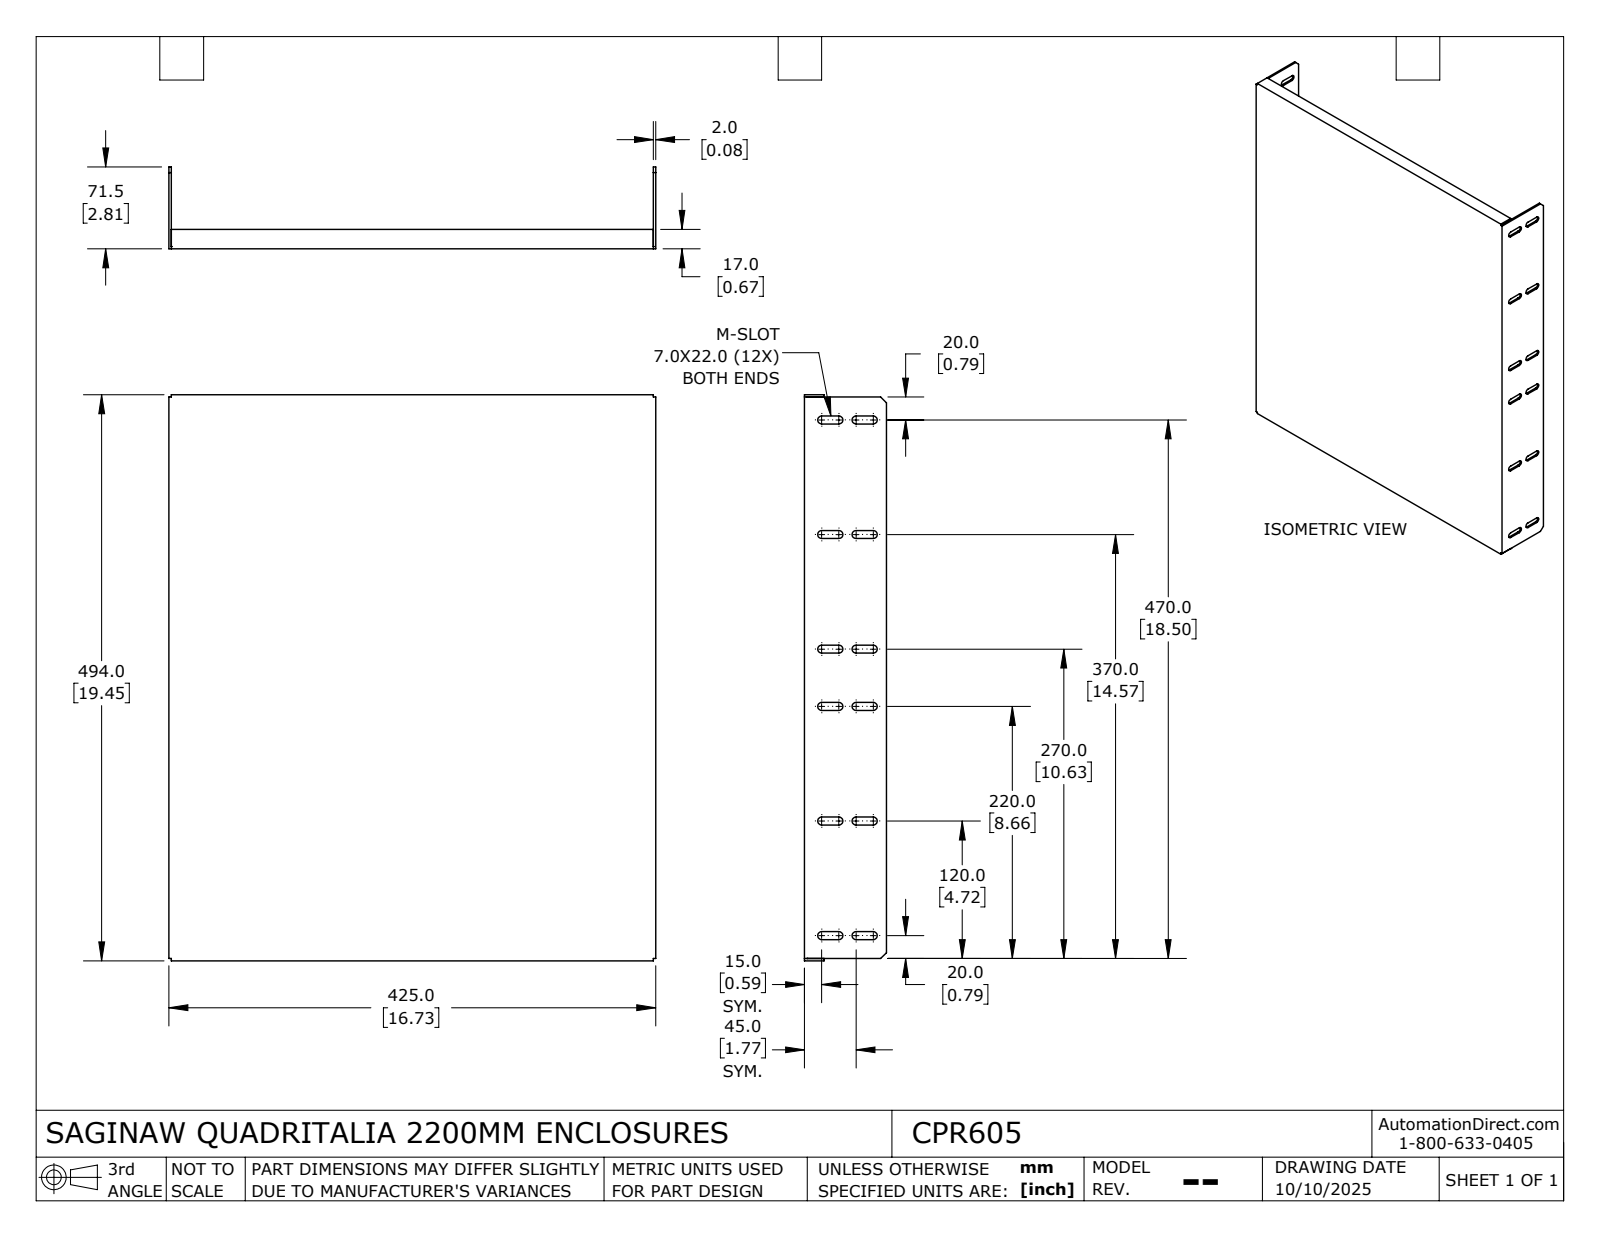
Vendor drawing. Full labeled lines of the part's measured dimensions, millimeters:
Part name (STEP PRODUCT): CPR605_Default
STEP written by: SolidWorks 2024 (CONFIG_CONTROL_DESIGN)
Units: millimetres
Bodies: 1 solid, 123 faces (75 planar, 48 cylindrical, 0 other)
Overall size (bounding box): 494 × 425 × 71.5
Volume: 574 359 mm³ · Surface area: 581 184 mm²
Partial cylindrical surfaces — rounded edges, fillets, slot ends (radius × count): R3.5 ×24
Main face-to-face distances: 2, 423, 425, 421, 492, 494, 490, 71.5, 69.5, 17
